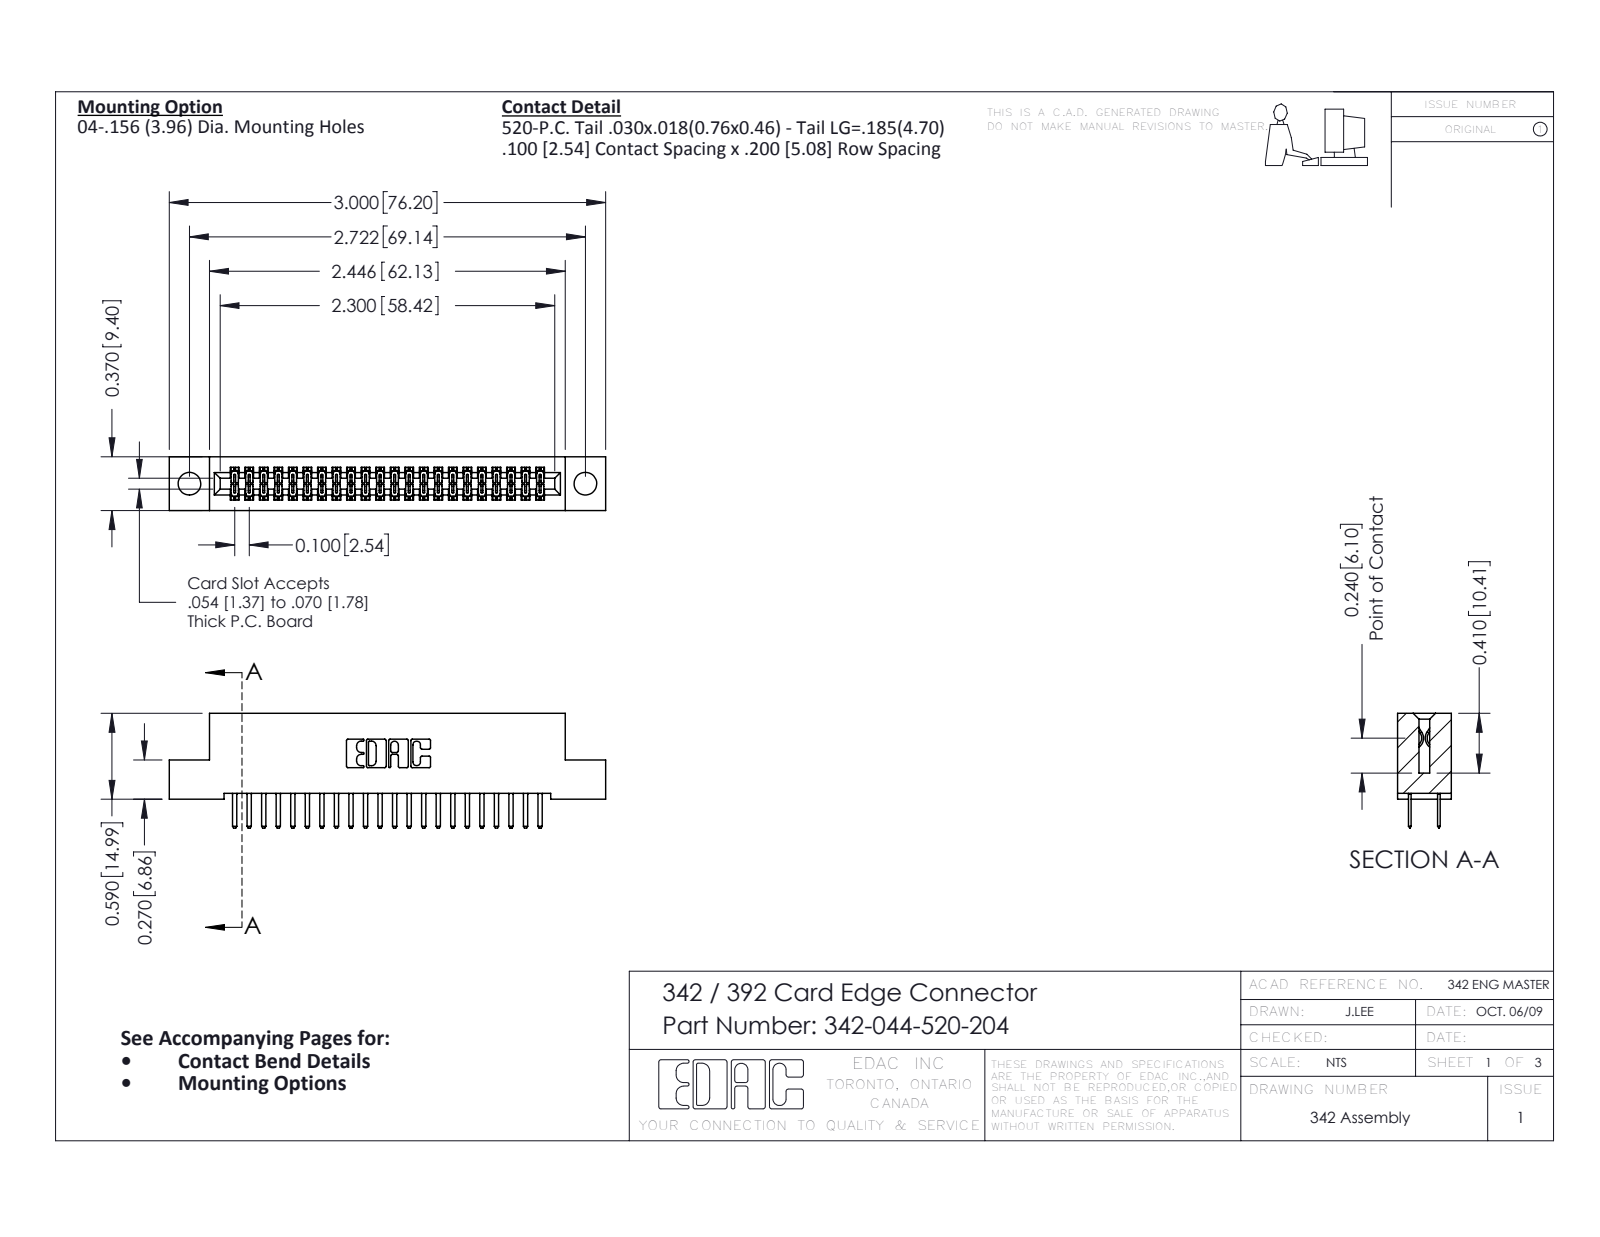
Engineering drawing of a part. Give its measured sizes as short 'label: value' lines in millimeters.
name: 342-044-520-204; 342 Part_.156 TH; 345-292-001_345-293-120
written by: SolidWorks 2016 (CONFIG_CONTROL_DESIGN)
unit: mm
bodies: 45 solids, 2574 faces (1738 planar, 836 cylindrical, 0 other)
size: 76.2 × 20 × 9.4
volume: 6 650 mm³; area: 10 100 mm²
holes: 2× ⌀4
rounds: 92× R0.3, 66× R0.2, 22× R0.3, 6× R0.2, 6× R0.8, 3× R0.7, 2× R0.4, 2× R0.6
face distances: 1.8, 7.6, 9.4, 5.1, 5.7, 1.9, 3.8, 5.6, 3.8, 0.6
hole spacings: 69.1
